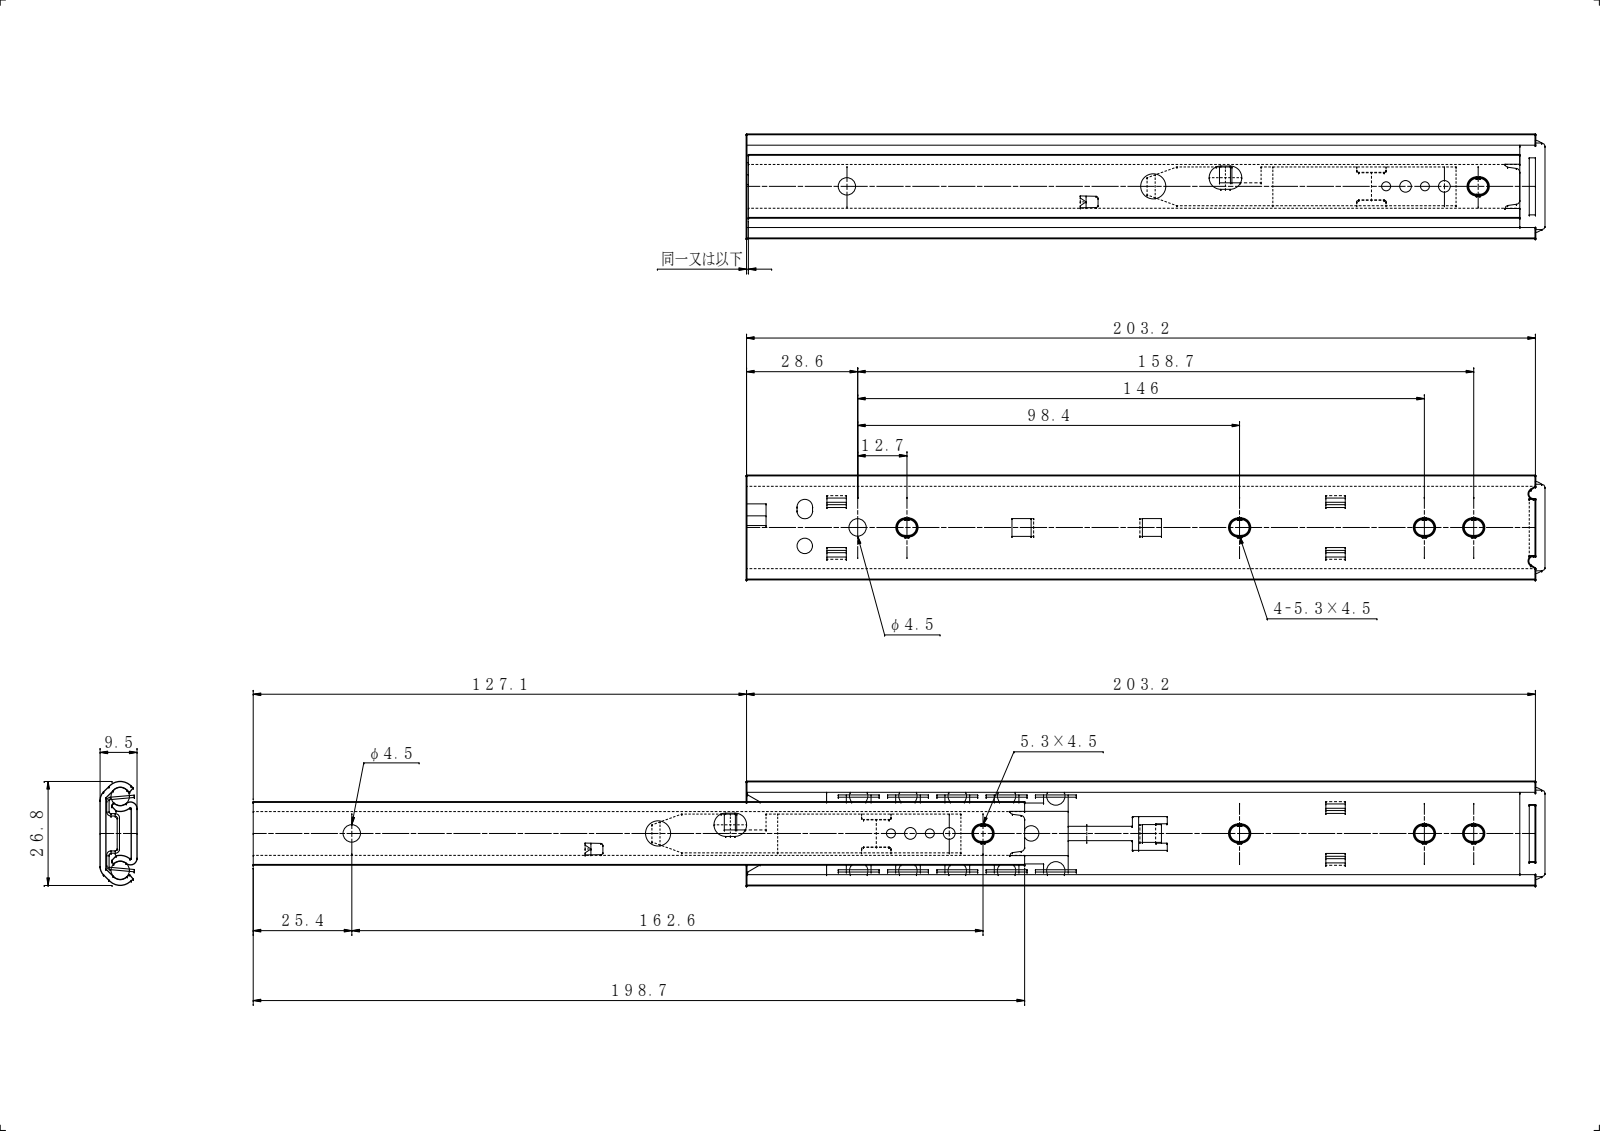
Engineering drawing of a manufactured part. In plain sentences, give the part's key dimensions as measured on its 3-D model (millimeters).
The part is named "PN101リベット; U2725-8; U2725-8 IM; U2725-8 OM (+3 more)". Its 3-D file was written by "SolidWorks 2019 (CONFIG_CONTROL_DESIGN)". It is 7 solids with 257 faces: 112 planar, 129 cylindrical and 16 other. Overall it measures 332.8 by 26.8 by 9.5 millimeters. Its volume is 20 547 cubic millimeters and its surface area 30 235 square millimeters. Round holes: 2 of diameter 2.34, 2 of diameter 3, 2 of diameter 3.03, 2 of diameter 4.2, 2 of diameter 4.5, 1 of diameter 4, 1 of diameter 6.5. Round bosses or shafts: 2 of diameter 4.5, 2 of diameter 4.3, 2 of diameter 3.9, 2 of diameter 2.3. Partial cylindrical surfaces (rounded edges, fillets, slot ends): 12 of radius 0.2, 12 of radius 2, 10 of radius 2.25, 6 of radius 0.5, 5 of radius 3, 4 of radius 1, 2 of radius 0.18, 2 of radius 0.8. The main face-to-face distances are 1.5, 8, 6.5, 9.5, 0.6, 5.72, 1.68, 6.32, 7.82, 2.28. The hole center spacings are 5, 10, 8.6, 13.6, 14.49, 15, 18.6, 22.76.
